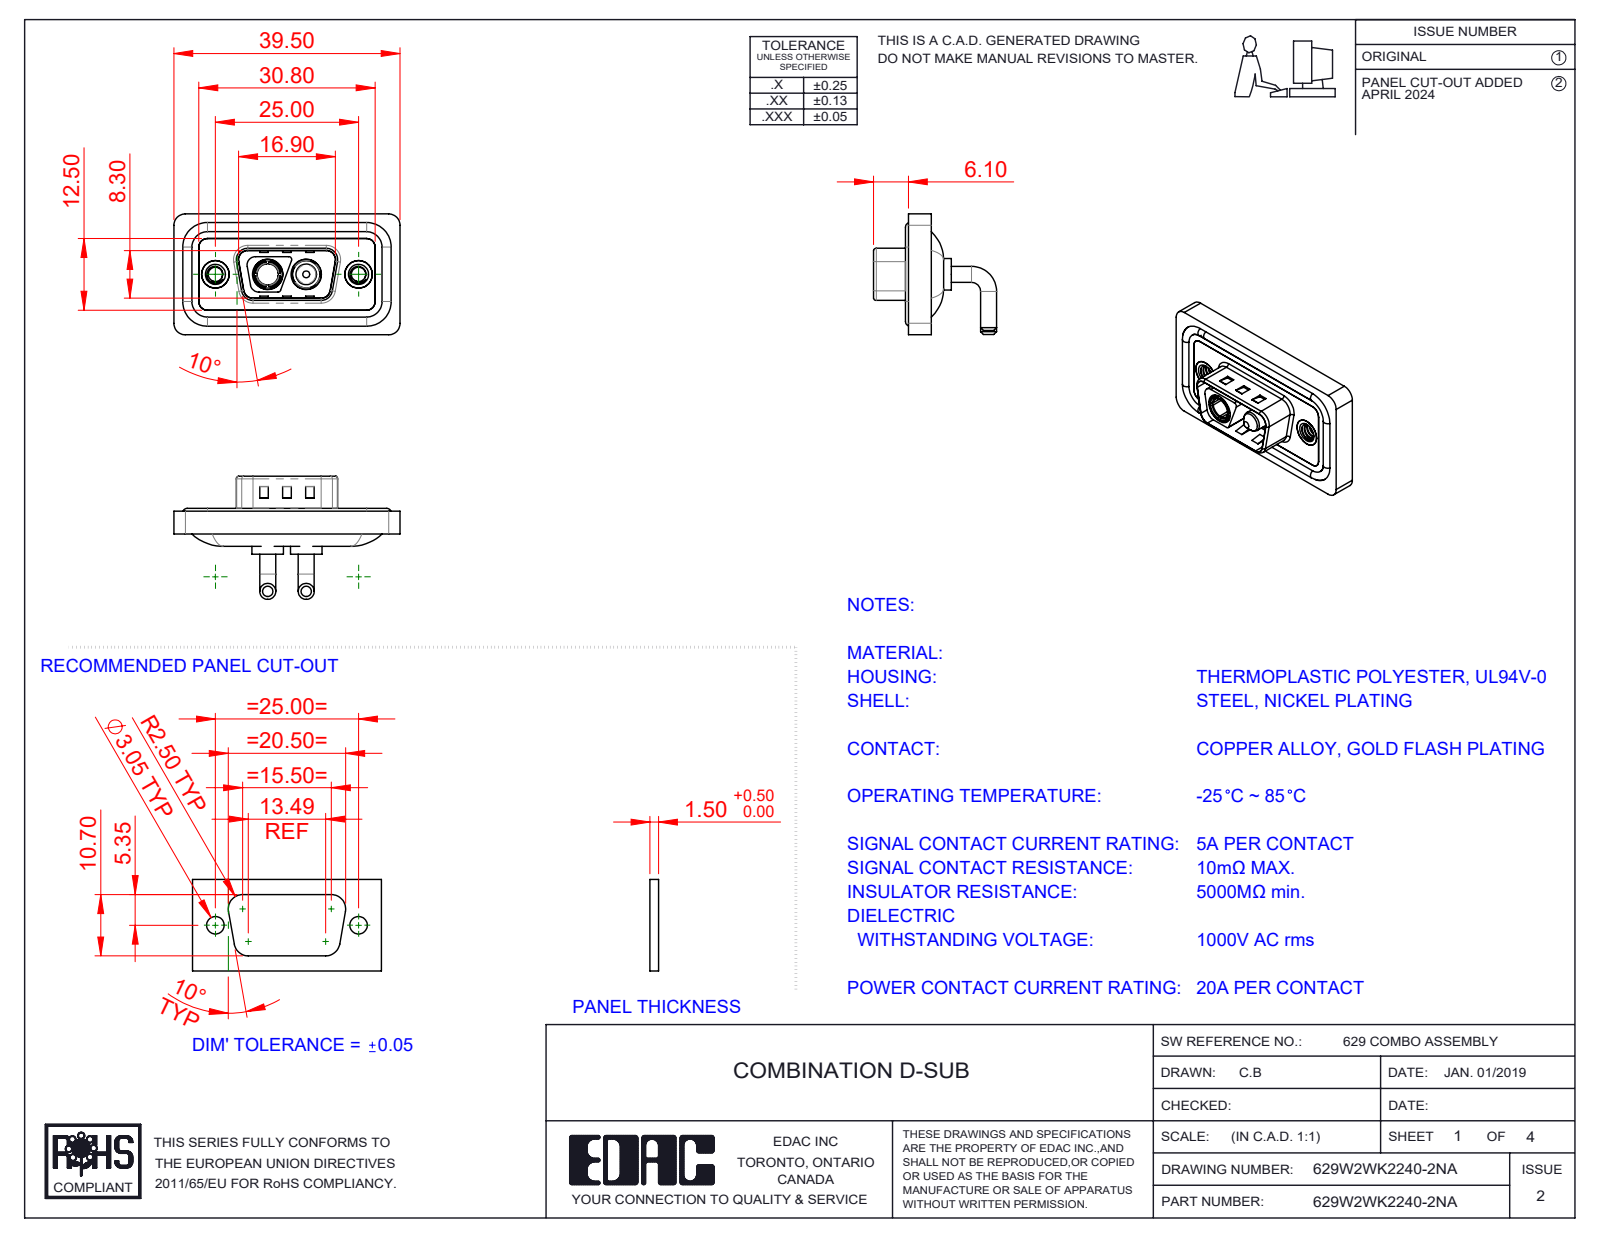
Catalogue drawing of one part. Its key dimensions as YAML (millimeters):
part_name: "629Combo Housing_2WK2; 629Combo Shell Front_09 Contacts; 629W2WK2140-2NA; 629Combo Shell Rear_09 Contacts (+4 more)"
step_written_by: "SolidWorks 2023 (CONFIG_CONTROL_DESIGN)"
units: millimeters
bodies: {solids: 11, faces: 536, planar: 189, cylindrical: 229, other: 118}
overall_size: [39.5, 21.5, 21.1]
volume: 4686
surface_area: 7536
round_holes:
  - {diameter: 2.5, count: 2}
  - {diameter: 4, count: 2}
  - {diameter: 4.8, count: 2}
  - {diameter: 4.85, count: 2}
  - {diameter: 5, count: 2}
  - {diameter: 5.3, count: 2}
  - {diameter: 3.7, count: 1}
round_bosses_or_shafts:
  - {diameter: 2.8, count: 4}
  - {diameter: 1.6, count: 4}
  - {diameter: 5.5, count: 2}
  - {diameter: 5.2, count: 2}
  - {diameter: 4.9, count: 2}
  - {diameter: 4.75, count: 2}
  - {diameter: 3.75, count: 2}
  - {diameter: 4.96, count: 1}
partial_cylinders:
  - {radius: 1.5, count: 20}
  - {radius: 2, count: 18}
  - {radius: 0.5, count: 10}
  - {radius: 1.6, count: 8}
  - {radius: 0.25, count: 4}
  - {radius: 0.6, count: 4}
  - {radius: 0.65, count: 4}
  - {radius: 0.9, count: 4}
face_to_face_distances: [0.4, 2.9, 1.1, 0.8, 2.1, 2.5, 3.1, 1.6, 4.5, 1.5]
hole_center_spacings: [9.14, 15.86, 6.72, 25]
